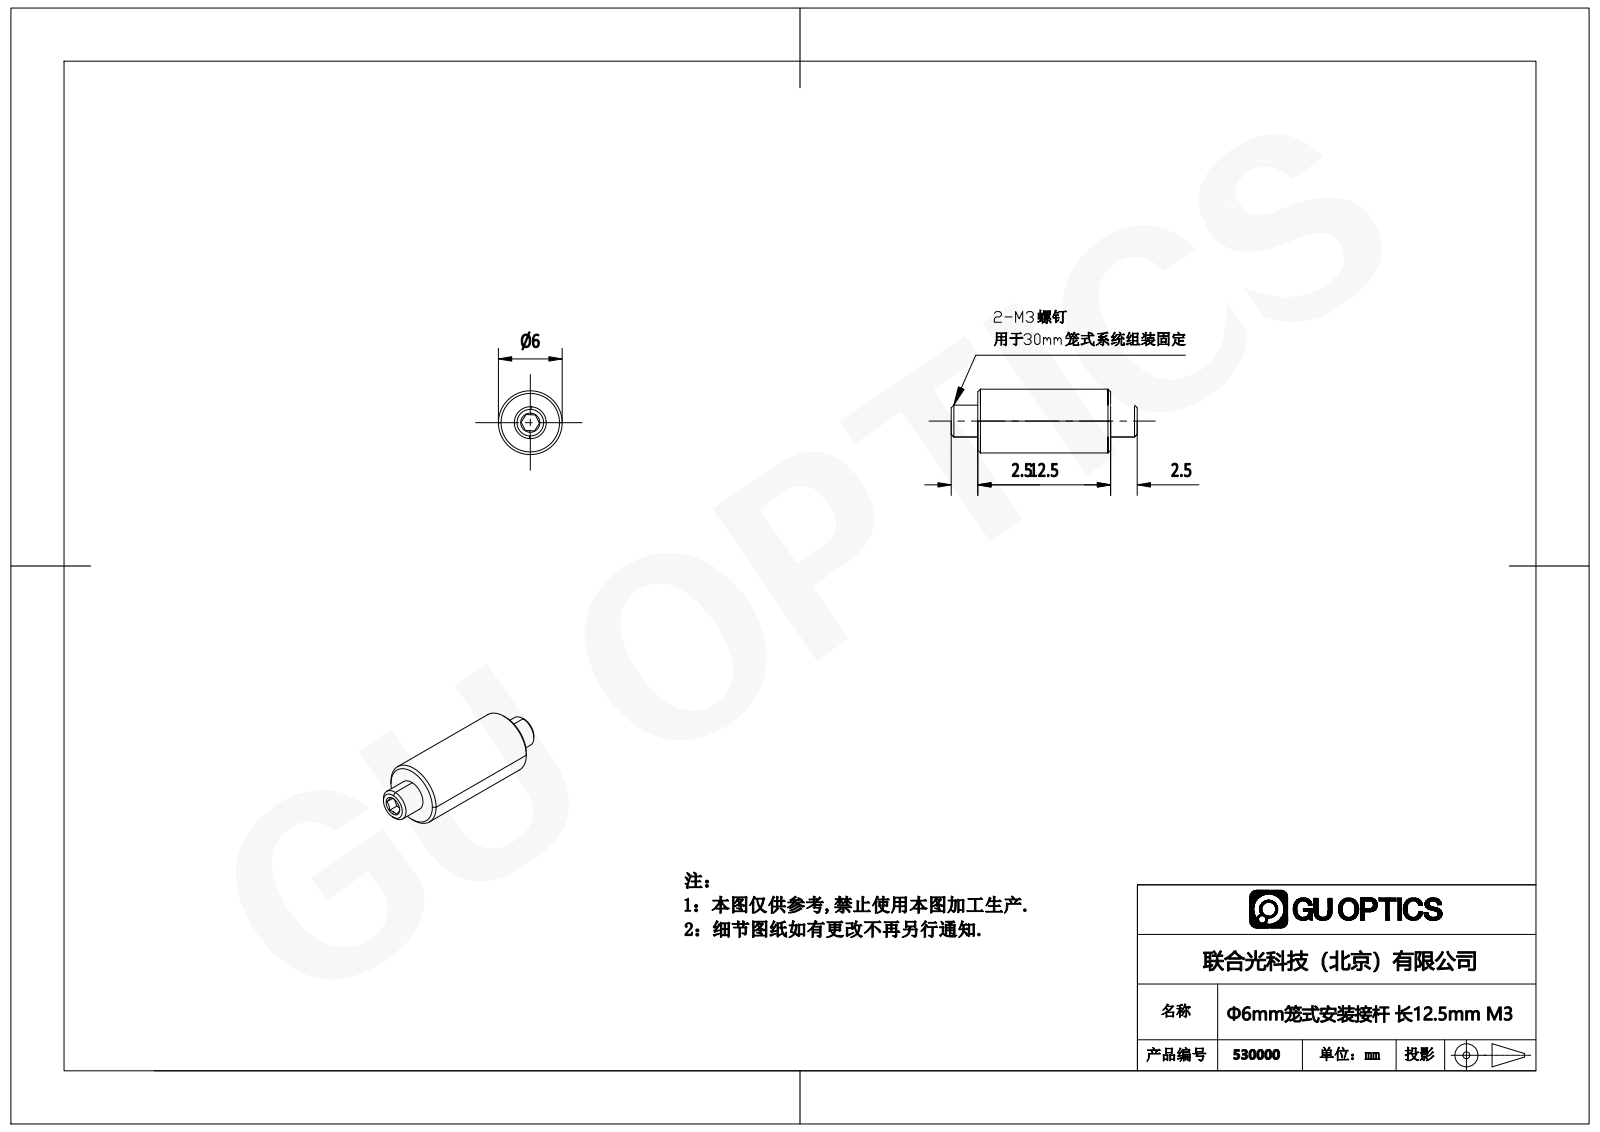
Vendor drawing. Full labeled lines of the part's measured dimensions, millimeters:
STEP written by: SolidWorks 2018 (AUTOMOTIVE_DESIGN)
Units: millimetres
Bodies: 0 solids, 36 faces (18 planar, 6 cylindrical, 12 other)
Overall size (bounding box): 17.5 × 6 × 6
Round bosses / shafts (diameter × count): ⌀6 ×1, ⌀3 ×1
Main face-to-face distances: 12.5, 1.5, 2.5, 15, 1, 16.5, 14, 17.5, 15.5
